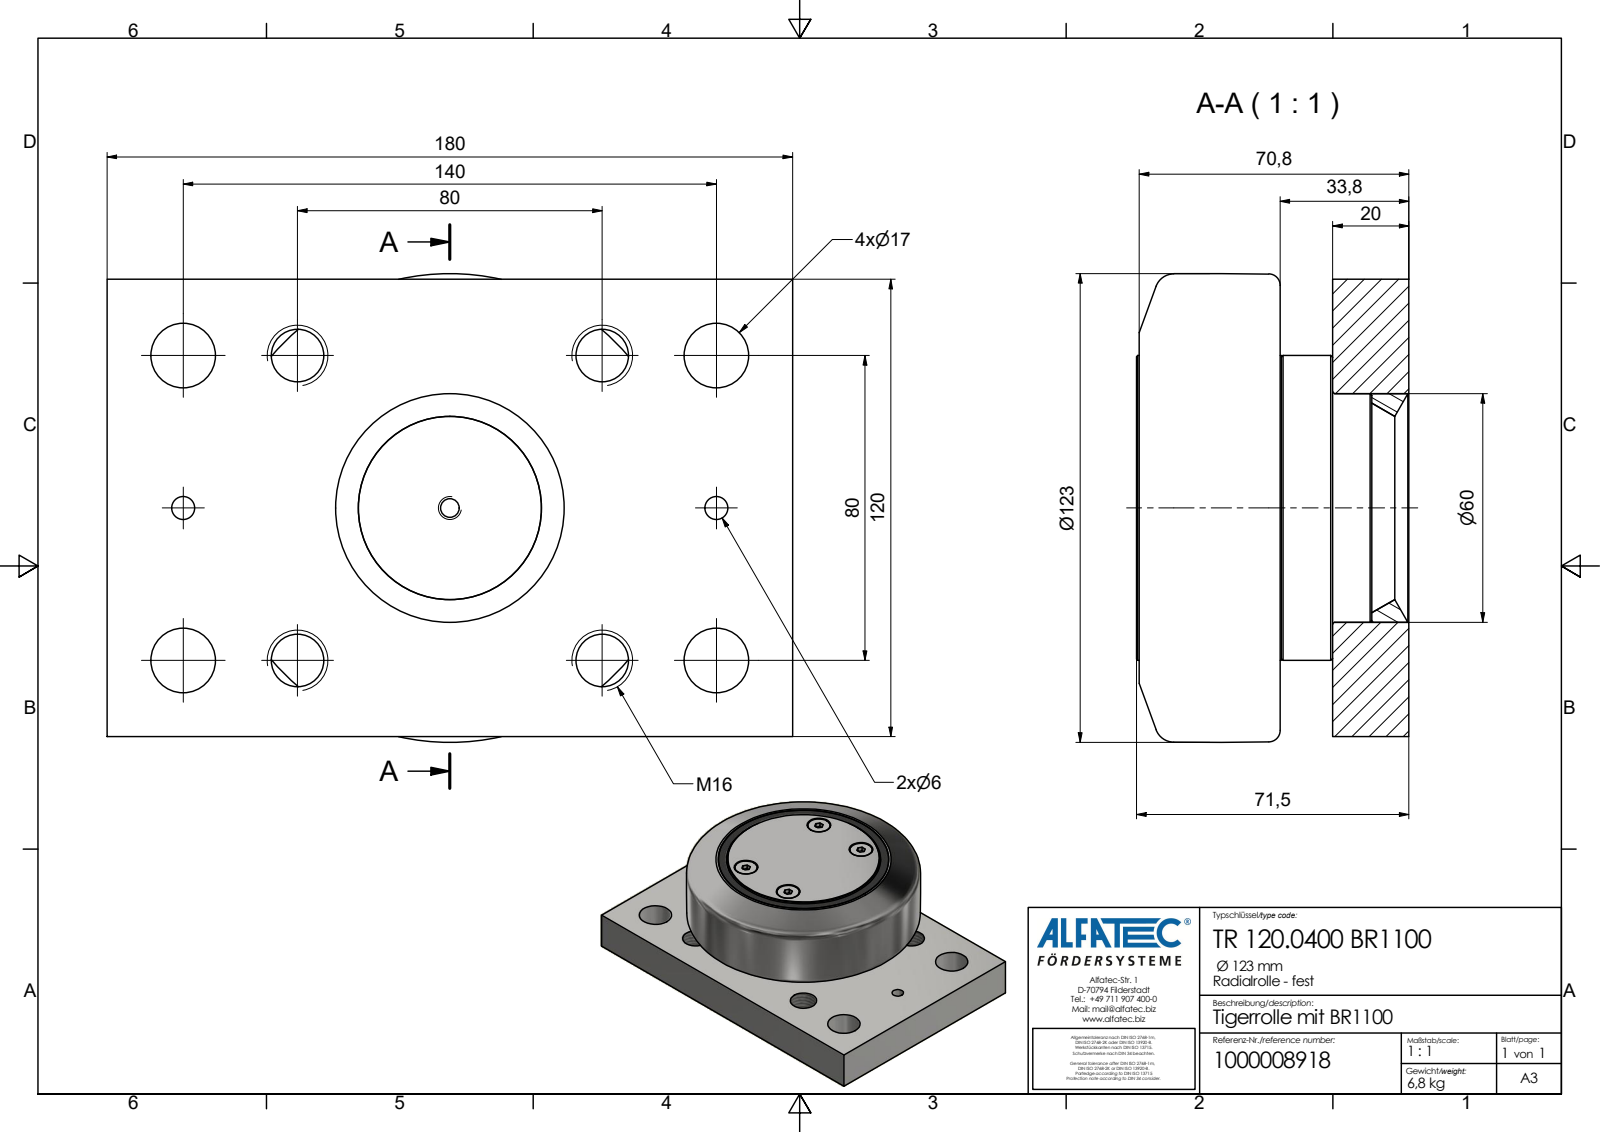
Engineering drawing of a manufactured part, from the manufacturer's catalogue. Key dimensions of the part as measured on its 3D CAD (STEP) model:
Part name (STEP PRODUCT): TR 120.0400 BR1100_Kontur
STEP written by: Autodesk Inventor 2020 (AP242_MANAGED_MODEL_BASED_3D_ENGINEERING_MIM_LF)
Units: millimetres
Bodies: 1 solid, 74 faces (46 planar, 21 cylindrical, 7 other)
Overall size (bounding box): 180 × 123 × 71.5
Volume: 895 443 mm³ · Surface area: 89 974 mm²
Round holes (diameter × count): ⌀12.4 ×4, ⌀13.84 ×4, ⌀17 ×4, ⌀6 ×2
Round bosses / shafts (diameter × count): ⌀11.7 ×4, ⌀80 ×1
Main face-to-face distances: 20, 33.8, 13.8, 71.5, 51.5, 37.7, 120, 180, 70.8, 50.8
Hole centre spacings: 80, 27.6, 30, 40, 50, 55.9, 57.11, 60.74
